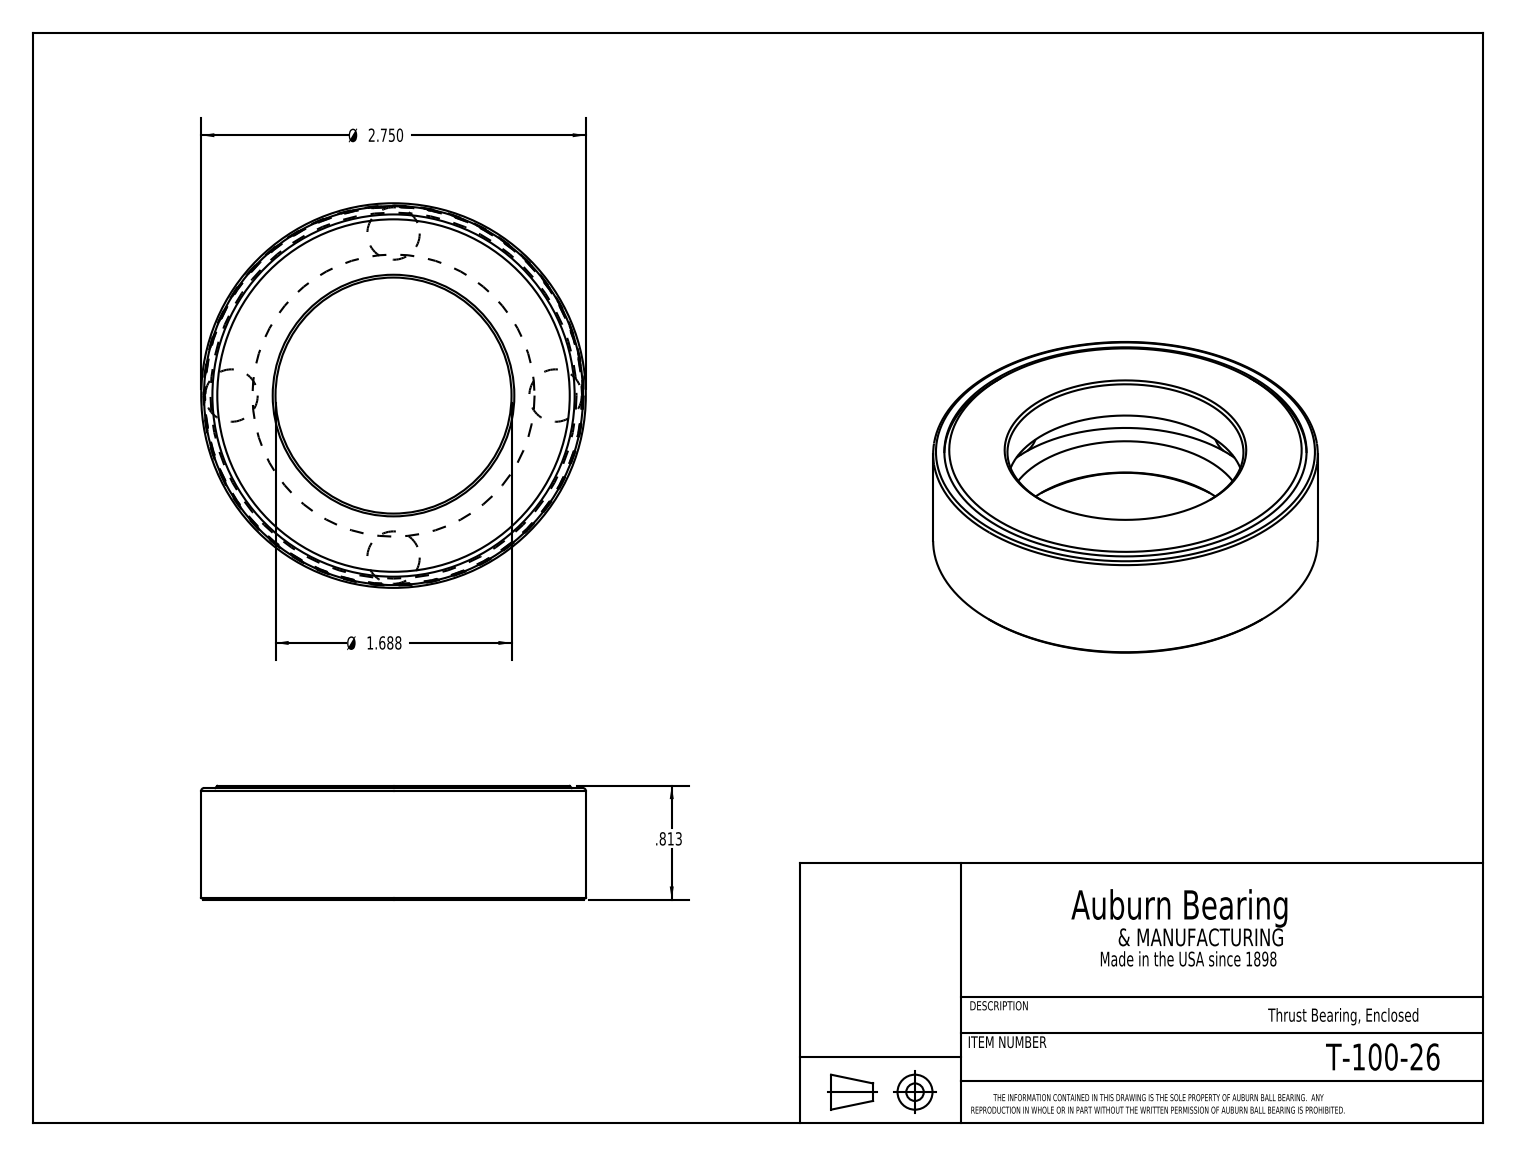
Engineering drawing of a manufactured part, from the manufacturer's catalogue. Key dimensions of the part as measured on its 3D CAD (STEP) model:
Part name (STEP PRODUCT): T-100-26
STEP written by: SolidWorks 2016 (CONFIG_CONTROL_DESIGN)
Units: inches
Bodies: 6 solids, 28 faces (9 planar, 7 cylindrical, 12 other)
Overall size (bounding box): 2.75 × 2.75 × 0.813
Volume: 2.05 in³ · Surface area: 33.92 in²
Round holes (diameter × count): ⌀1.687 ×1, ⌀2.59 ×1, ⌀2.71 ×1
Round bosses / shafts (diameter × count): ⌀2.75 ×1, ⌀2.696 ×1
Main face-to-face distances: 0.813, 0.294, 0.519, 0.225, 0.798, 0.504, 0.279, 0.015, 0.778, 0.484
